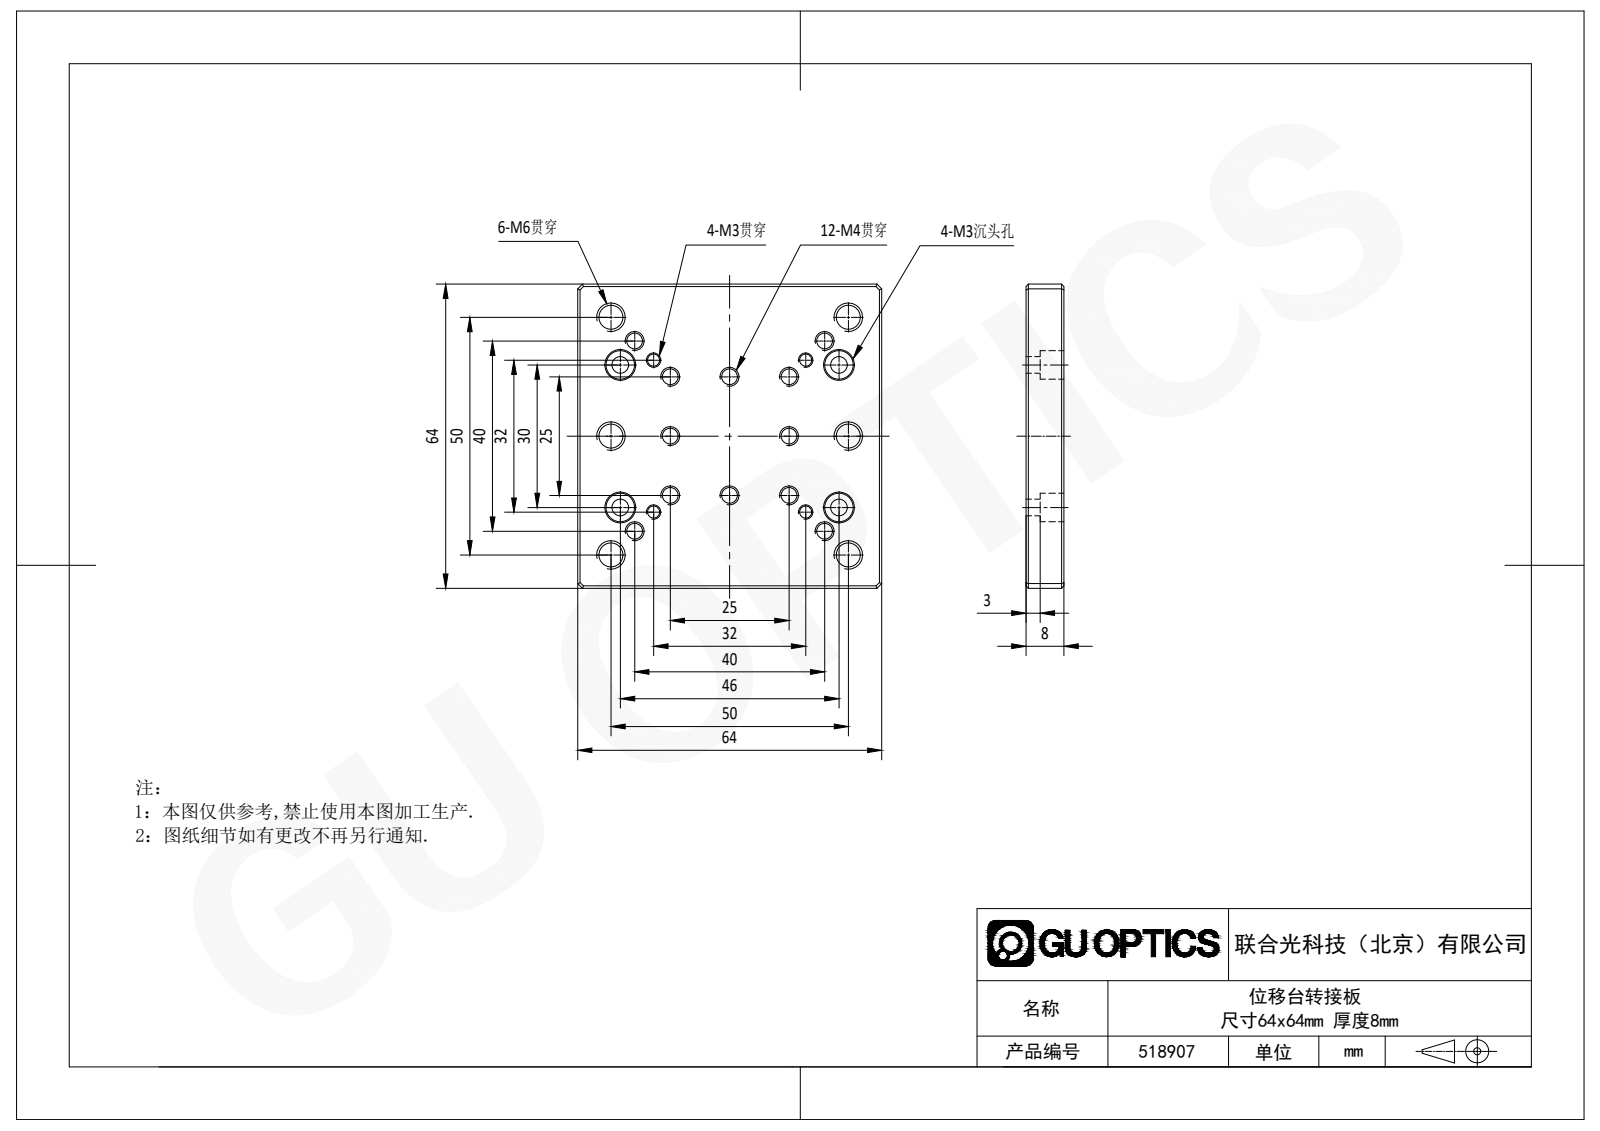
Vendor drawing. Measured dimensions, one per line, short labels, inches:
written by: SolidWorks 2020 (CONFIG_CONTROL_DESIGN)
unit: in
bodies: 1 solid, 86 faces (30 planar, 30 cylindrical, 26 other)
size: 2.52 × 2.52 × 0.315
volume: 1.834 in³; area: 18.53 in²
holes: 12× ⌀0.13, 6× ⌀0.197, 4× ⌀0.098, 4× ⌀0.138, 4× ⌀0.236
face distances: 0.315, 2.52, 1.976, 0.118, 0.197, 3.507, 2.675
hole spacings: 1.1, 0.696, 1.556, 0.492, 0.984, 0.278, 0.645, 0.841
